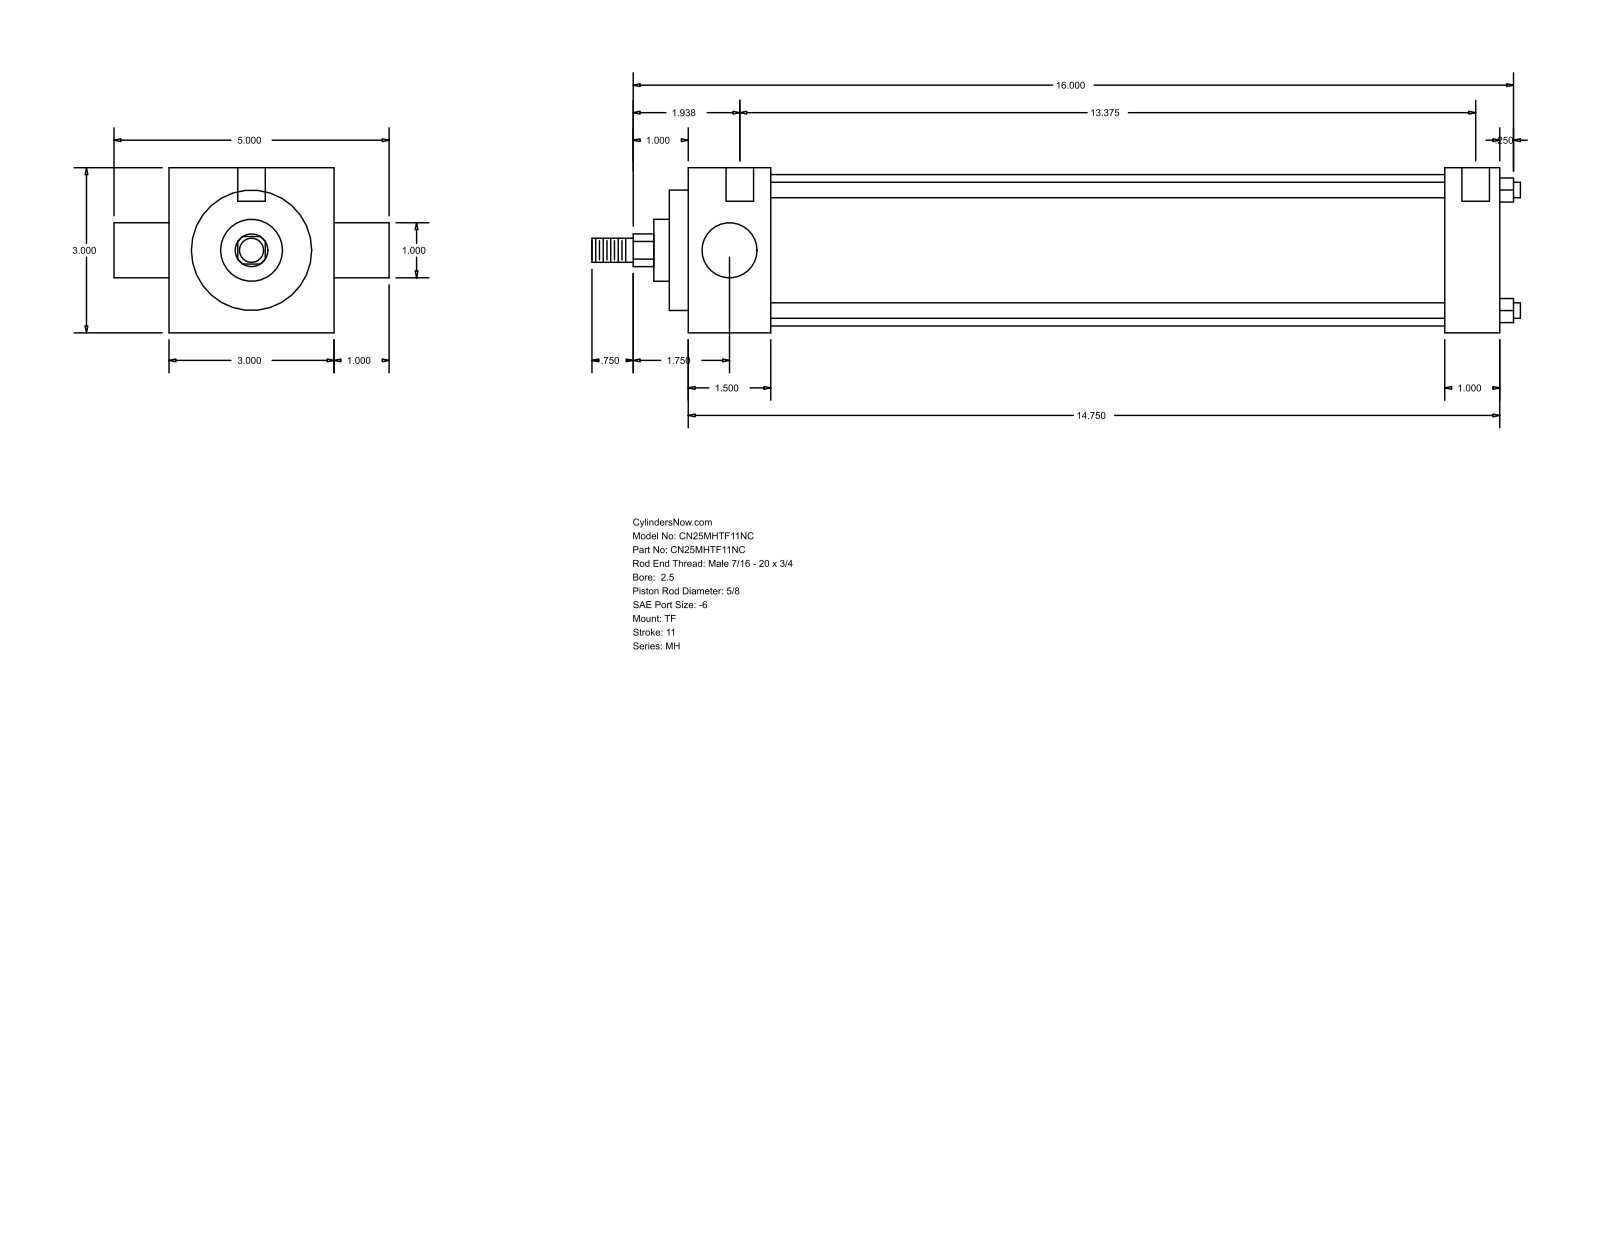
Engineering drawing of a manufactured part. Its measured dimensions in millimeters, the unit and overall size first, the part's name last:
Units: millimetres
Overall size (bounding box): 428.62 × 127 × 76.2
Round holes (diameter × count): ⌀5.56 ×3, ⌀12.7 ×2
Round bosses / shafts (diameter × count): ⌀7.14 ×4, ⌀69.85 ×1, ⌀55.55 ×1, ⌀28.57 ×1, ⌀25.4 ×1, ⌀15.88 ×1, ⌀11.11 ×1
Partial cylindrical surfaces — rounded edges, fillets, slot ends (radius × count): R7.54 ×1
Main face-to-face distances: 76.2, 374.65, 25.4, 38.1, 336.55, 349.25, 311.15, 8.73, 46.83, 357.98
Hole centre spacings: 3.17, 4.76, 339.73, 342.9, 344.49, 347.66
Bodies: 0 solids, 86 faces (61 planar, 25 cylindrical, 0 other)
Part name (STEP PRODUCT): MH_TF__0250_0.625
STEP written by: GSSL Pune (CONFIG_CONTROL_DESIGN)
